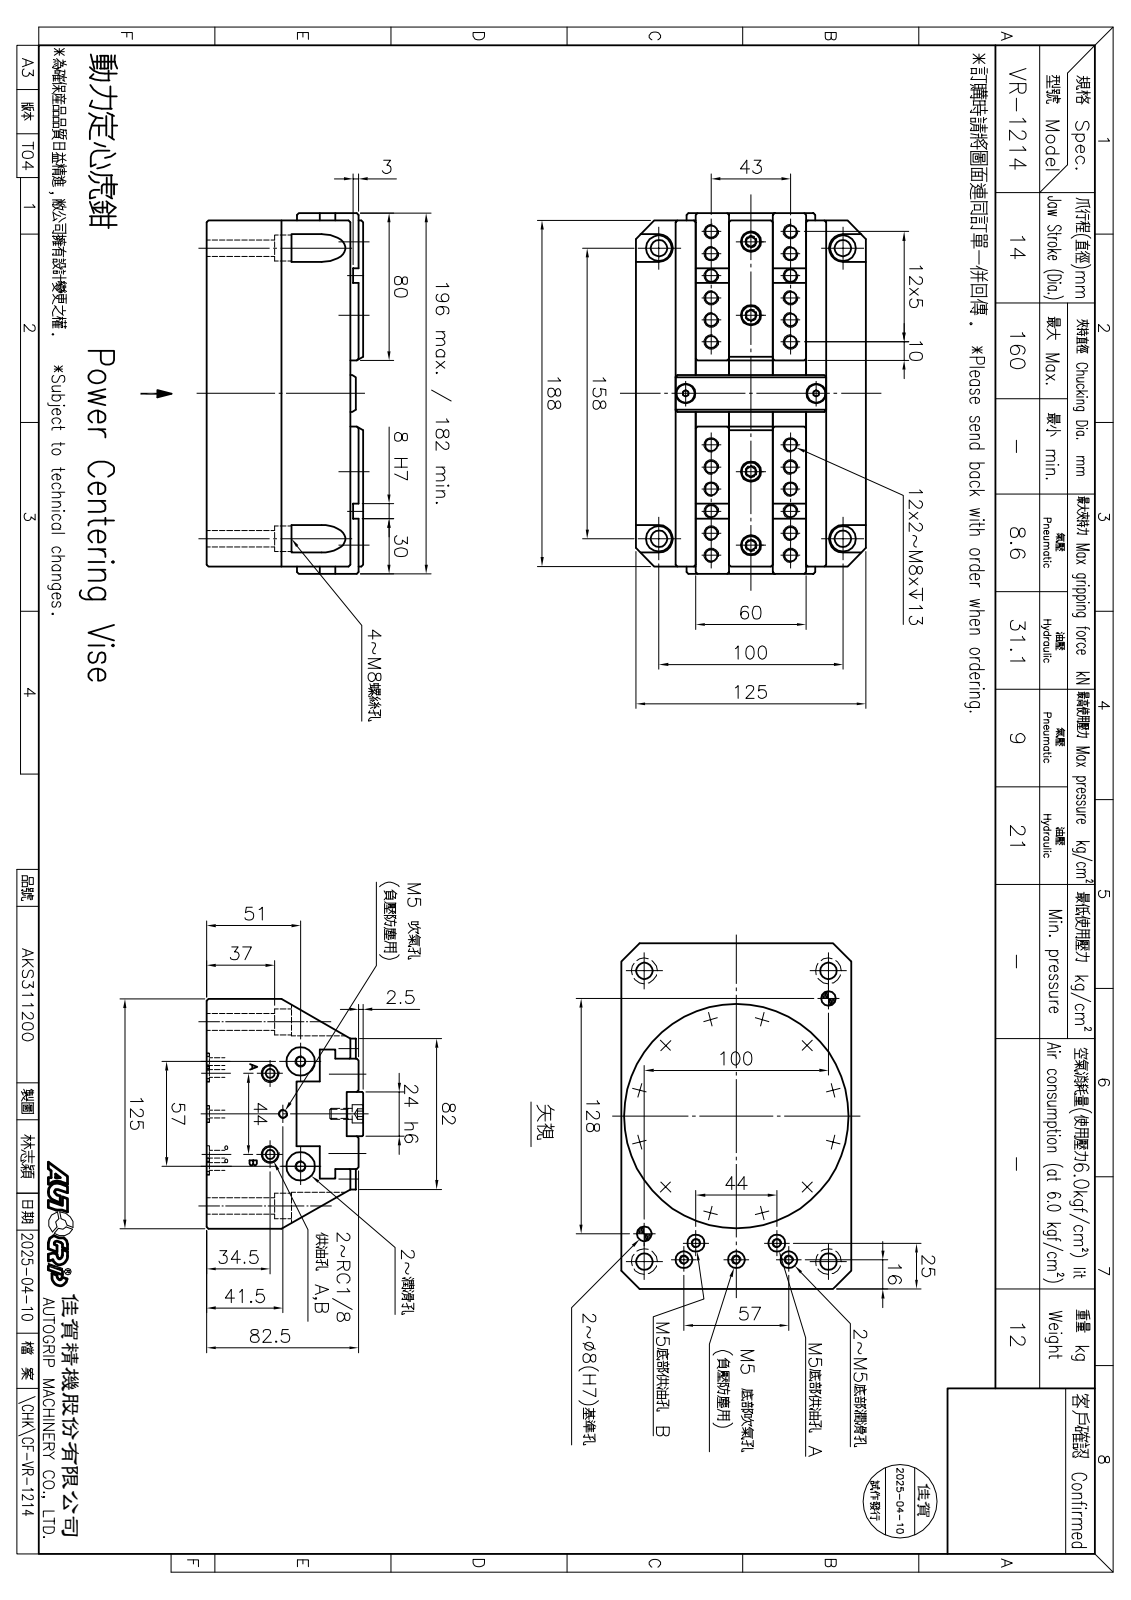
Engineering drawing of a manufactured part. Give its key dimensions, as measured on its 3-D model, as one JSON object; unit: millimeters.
{"part_name": "CF-VR-1214-01000; CF-VR-1214-06000; 圓頭內六角螺栓_M6x12; 無頭六角孔螺絲_M5x6 (+8 more)", "step_written_by": "SolidWorks 2020 (CONFIG_CONTROL_DESIGN)", "units": "millimeters", "bodies": {"solids": 44, "faces": 915, "planar": 550, "cylindrical": 179, "other": 186}, "overall_size": [196, 125, 85.25], "volume_mm3": 1658000, "surface_area_mm2": 236892, "round_holes": [[6.8, 24], [4.2, 20], [5.5, 12], [9.5, 12], [5, 8], [9.2, 5], [6.6, 4], [9, 4], [11, 4], [14, 4], [2.5, 2], [5.6, 2]], "round_bosses_or_shafts": [[5, 20], [8.5, 14], [10, 6], [6, 6], [12.5, 2], [3, 2]], "partial_cylinders_radius": [[4.25, 4], [7.5, 4]], "face_to_face_distances": [10, 12.5, 61.5, 51.5, 80, 45, 76, 14.5, 66, 21], "hole_center_spacings": [54.5, 94.4, 28.21, 54.51, 77.07, 105.29, 22.2, 28.22]}
